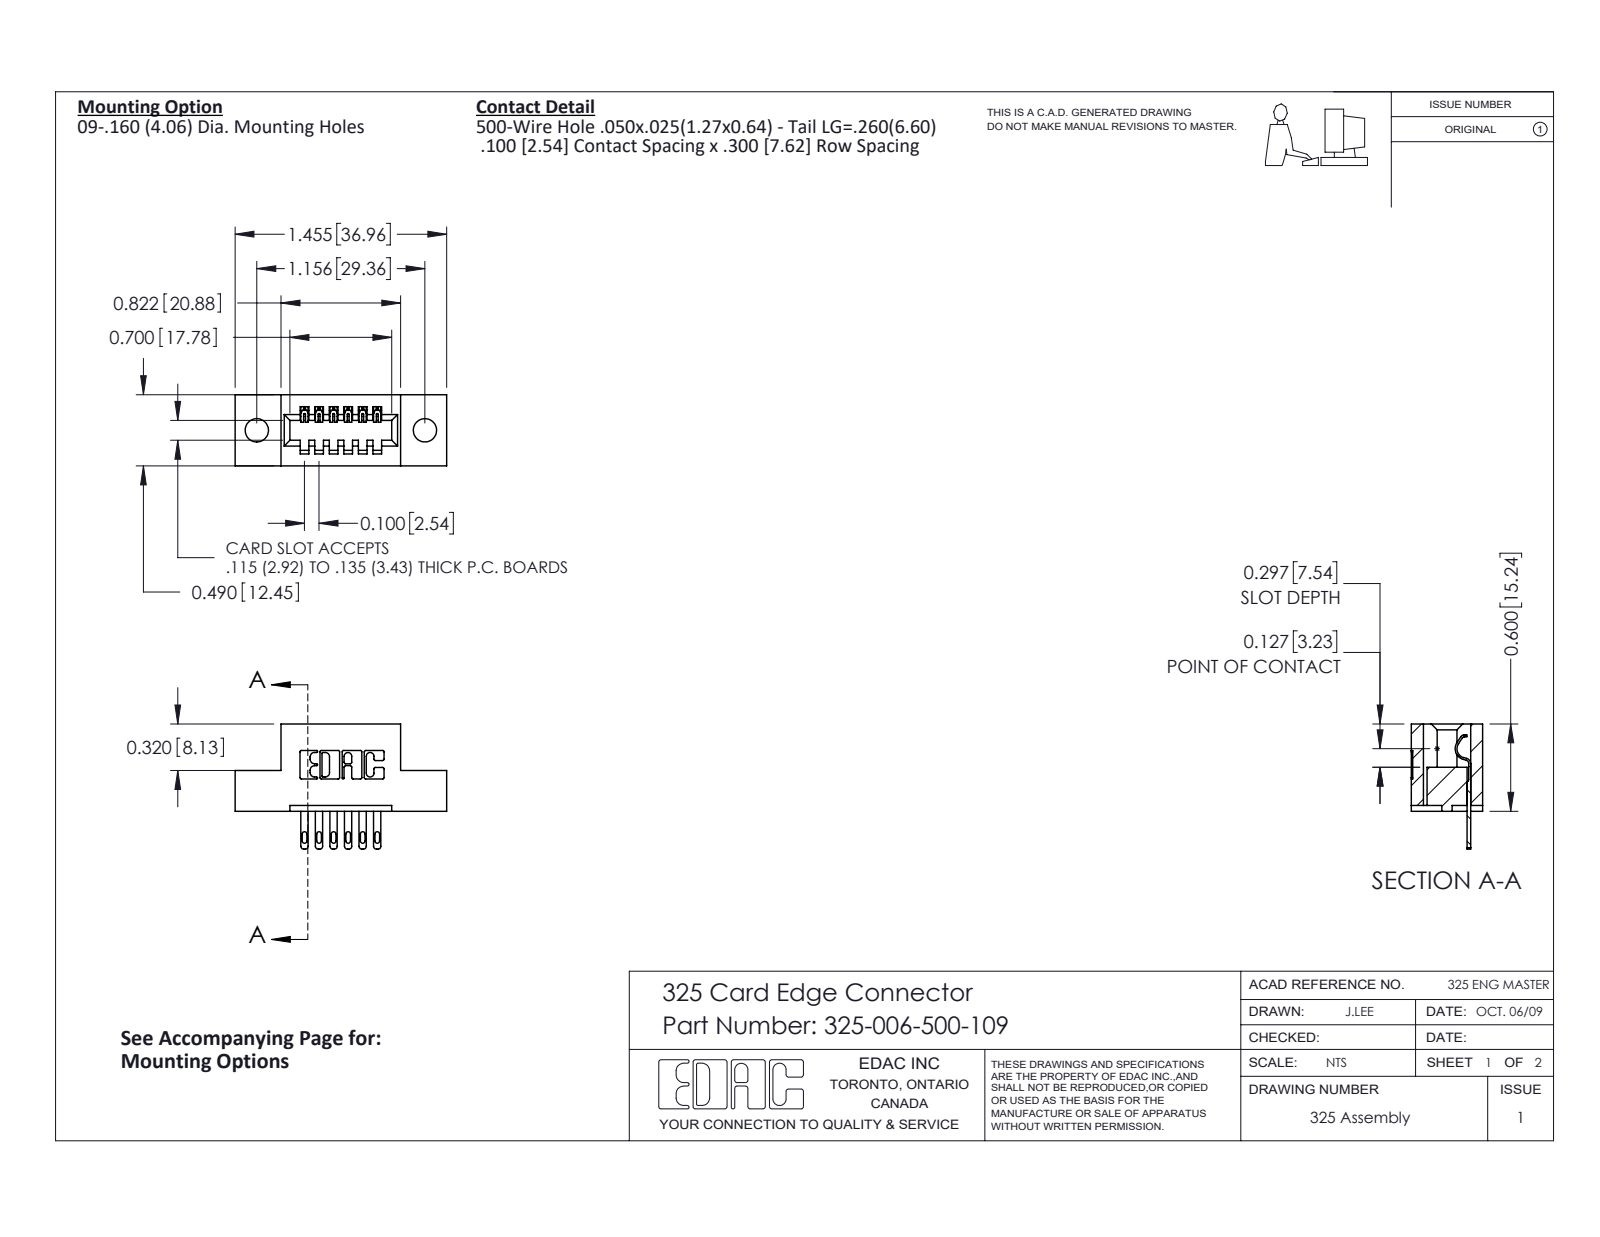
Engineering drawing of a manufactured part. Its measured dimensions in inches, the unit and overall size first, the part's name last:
Units: inches
Overall size (bounding box): 1.455 × 0.86 × 0.49
Round holes (diameter × count): ⌀0.16 ×2
Partial cylindrical surfaces — rounded edges, fillets, slot ends (radius × count): R0.01 ×22, R0.006 ×12, R0.016 ×12, R0.02 ×12, R0.007 ×6, R0.031 ×6, R0.026 ×3, R0.014 ×1
Main face-to-face distances: 0.3, 0.1, 0.04, 0.49, 0.2, 0.083, 0.407, 0.06, 0.16, 0.107
Hole centre spacings: 1.156
Volume: 0.255 in³ · Surface area: 5.994 in²
Bodies: 7 solids, 438 faces (286 planar, 152 cylindrical, 0 other)
Part name (STEP PRODUCT): 325-292-001_325-293-100; 325 Part_.160 TH; 325-006-500-109
STEP written by: SolidWorks 2016 (CONFIG_CONTROL_DESIGN)
